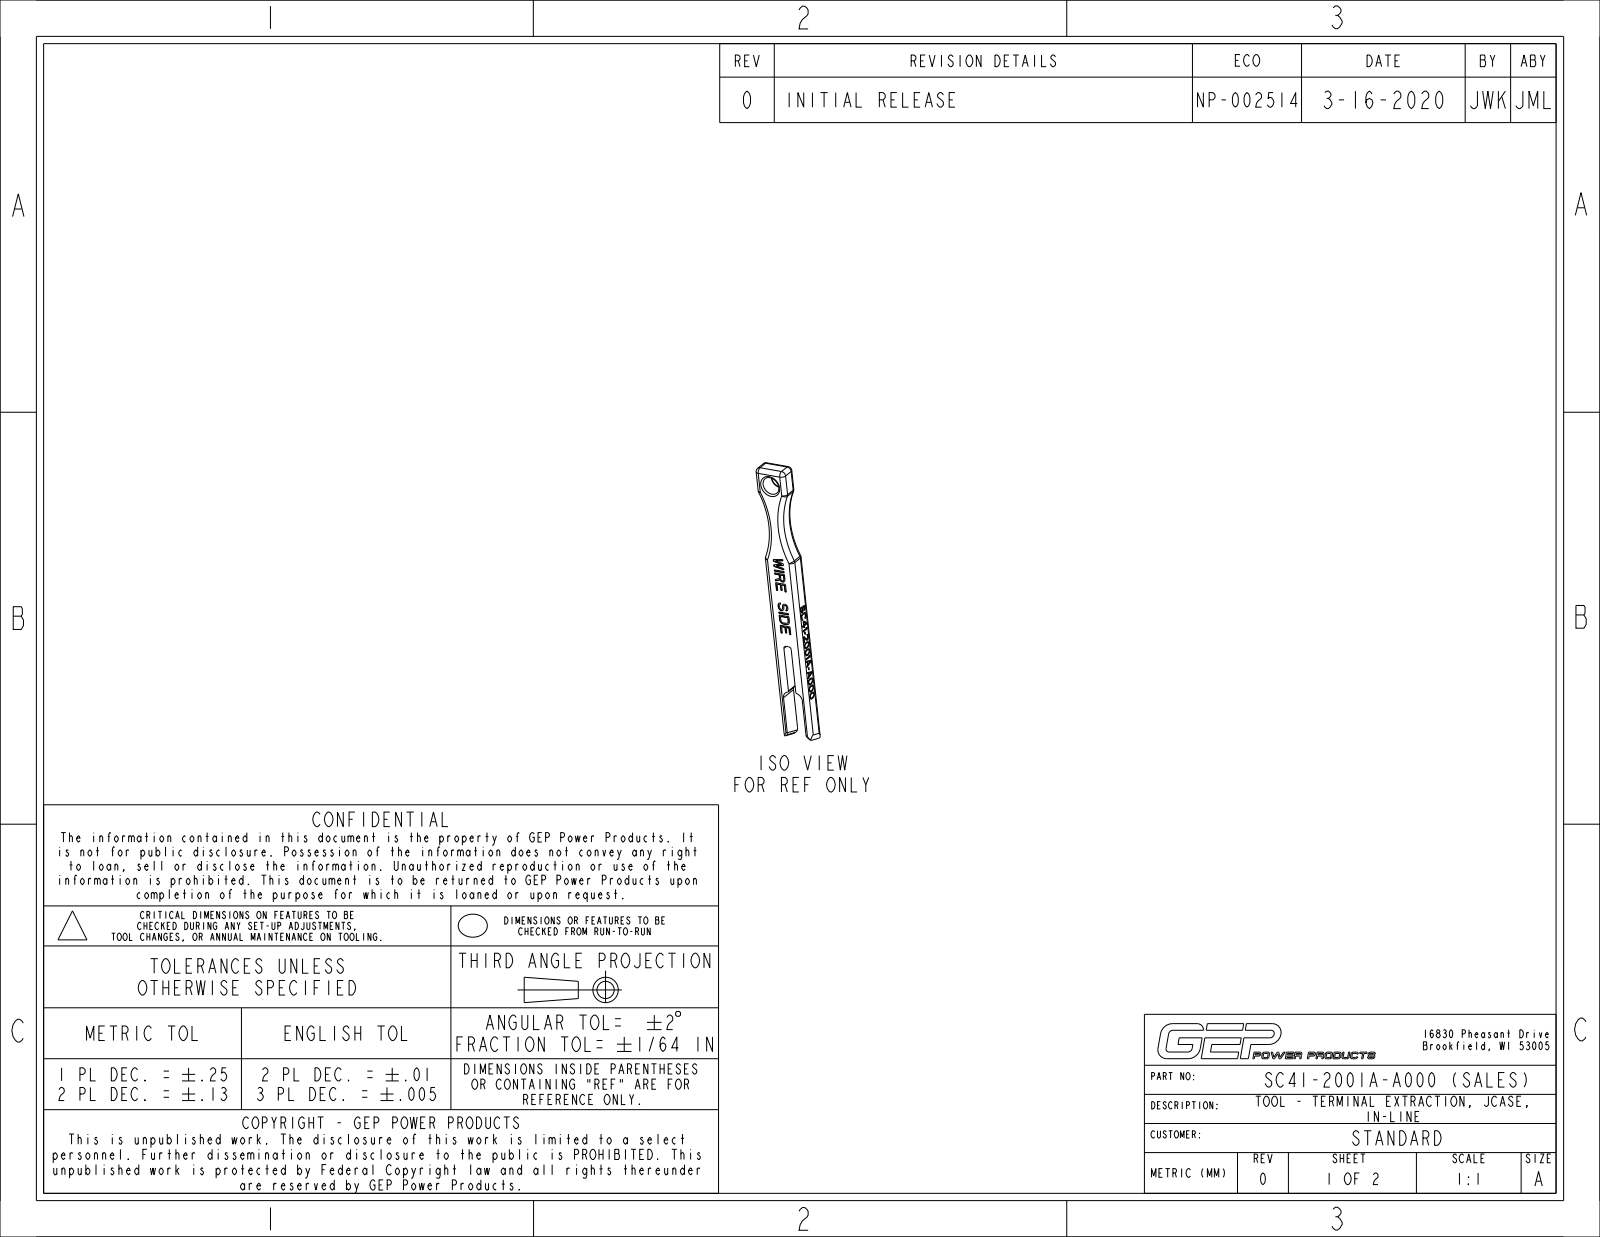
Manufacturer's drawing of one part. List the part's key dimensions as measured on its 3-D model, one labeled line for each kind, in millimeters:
Part name (STEP PRODUCT): PC41-2001A-A000_NCF; SC41-2001A-A000_NCF_ASM
STEP written by: CREO PARAMETRIC BY PTC INC, 2017110 (CONFIG_CONTROL_DESIGN)
Units: millimetres
Bodies: 1 solid, 908 faces (847 planar, 41 cylindrical, 20 other)
Overall size (bounding box): 52.84 × 5.9 × 3.39
Volume: 738 mm³ · Surface area: 953 mm²
Round holes (diameter × count): ⌀3.25 ×1
Partial cylindrical surfaces — rounded edges, fillets, slot ends (radius × count): R0.75 ×12, R0.5 ×6, R0.23 ×3, R0.64 ×3, R0.16 ×2, R0.25 ×2, R0.46 ×2, R1.3 ×2
Main face-to-face distances: 3.4, 5.9, 2.2, 3.7, 1.02, 2.68, 1.18, 4.88, 1.5, 3.86
